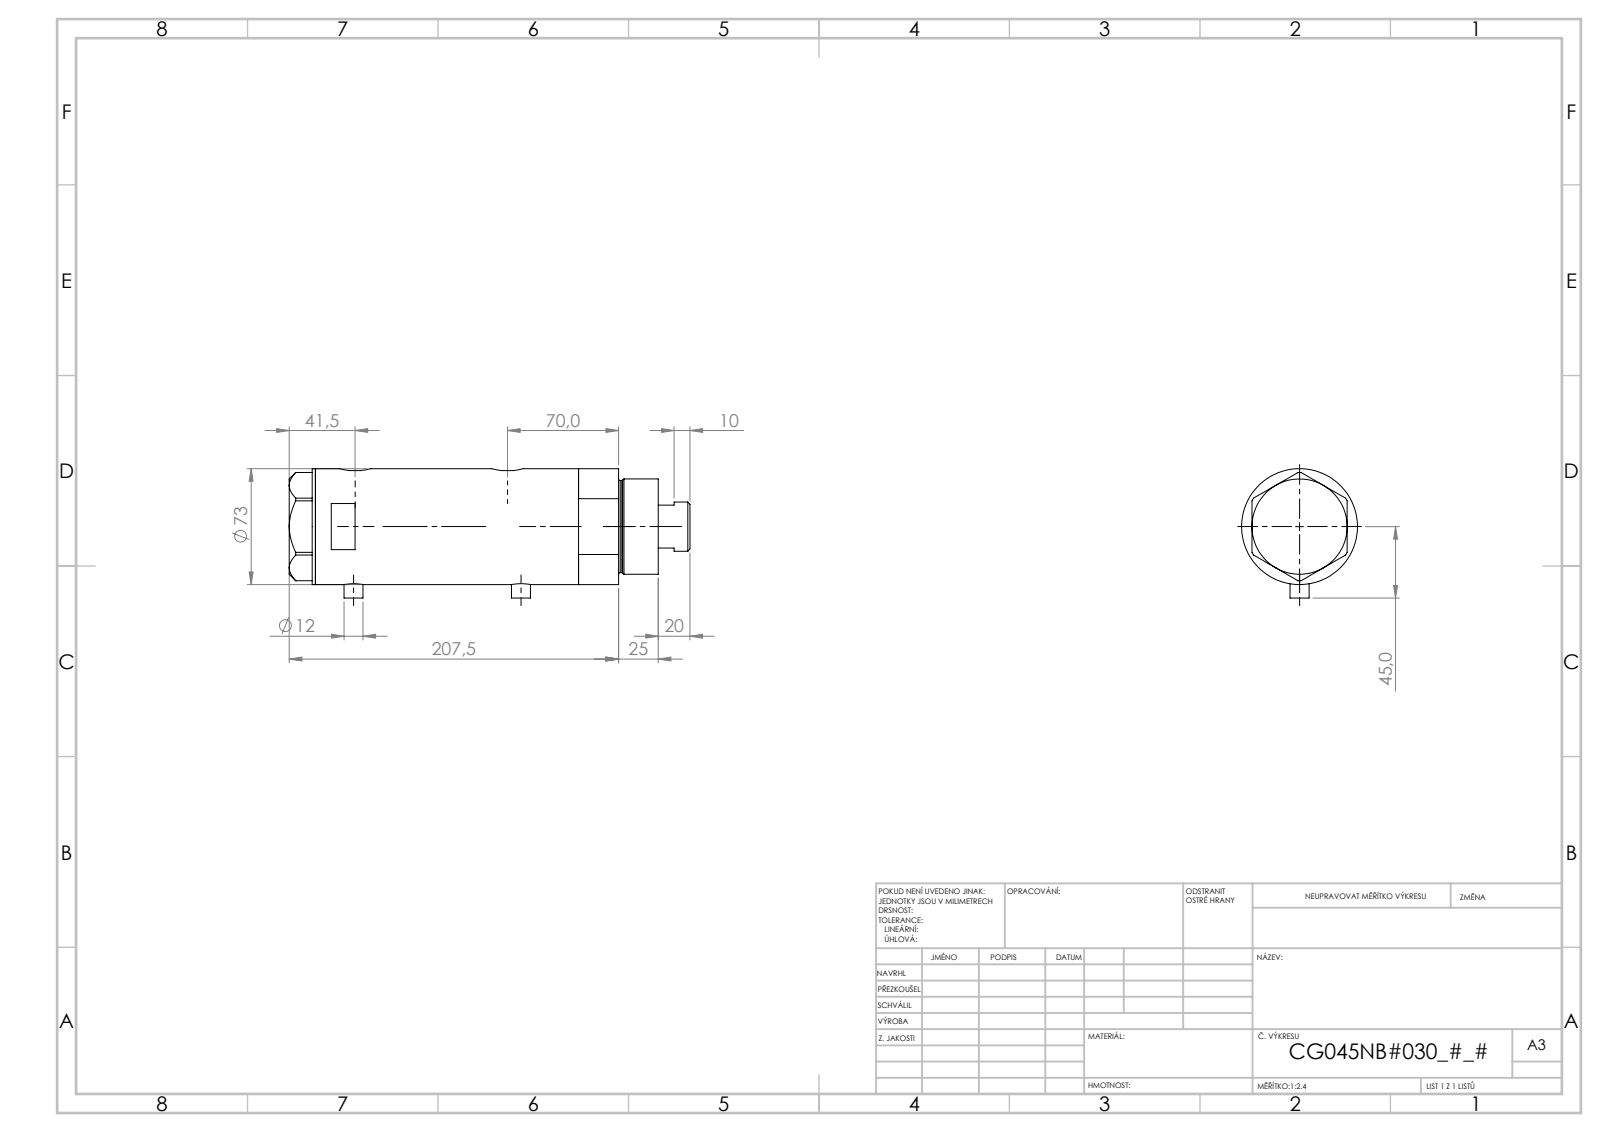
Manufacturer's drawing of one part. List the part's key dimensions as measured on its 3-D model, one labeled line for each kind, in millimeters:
Part name (STEP PRODUCT): V270CG_MIDDLE; V270CG_VC; V270CG_BACK; V270CG_FRONT
STEP written by: SolidWorks 2019 (CONFIG_CONTROL_DESIGN)
Units: millimetres
Bodies: 4 solids, 120 faces (49 planar, 51 cylindrical, 20 other)
Overall size (bounding box): 252.5 × 81.5 × 73
Volume: 901 868 mm³ · Surface area: 149 768 mm²
Round holes (diameter × count): ⌀12.5 ×2, ⌀13.16 ×2, ⌀10.5 ×1, ⌀32 ×1, ⌀33.5 ×1, ⌀45 ×1, ⌀48 ×1, ⌀64 ×1
Round bosses / shafts (diameter × count): ⌀12 ×2, ⌀73 ×1, ⌀60 ×1, ⌀58 ×1, ⌀31 ×1
Partial cylindrical surfaces — rounded edges, fillets, slot ends (radius × count): R10 ×2
Main face-to-face distances: 95, 121, 26, 16.5, 42.5, 137.5, 2, 216, 232.5, 190
Hole centre spacings: 1, 8.5, 96, 97, 104.5, 105.5
